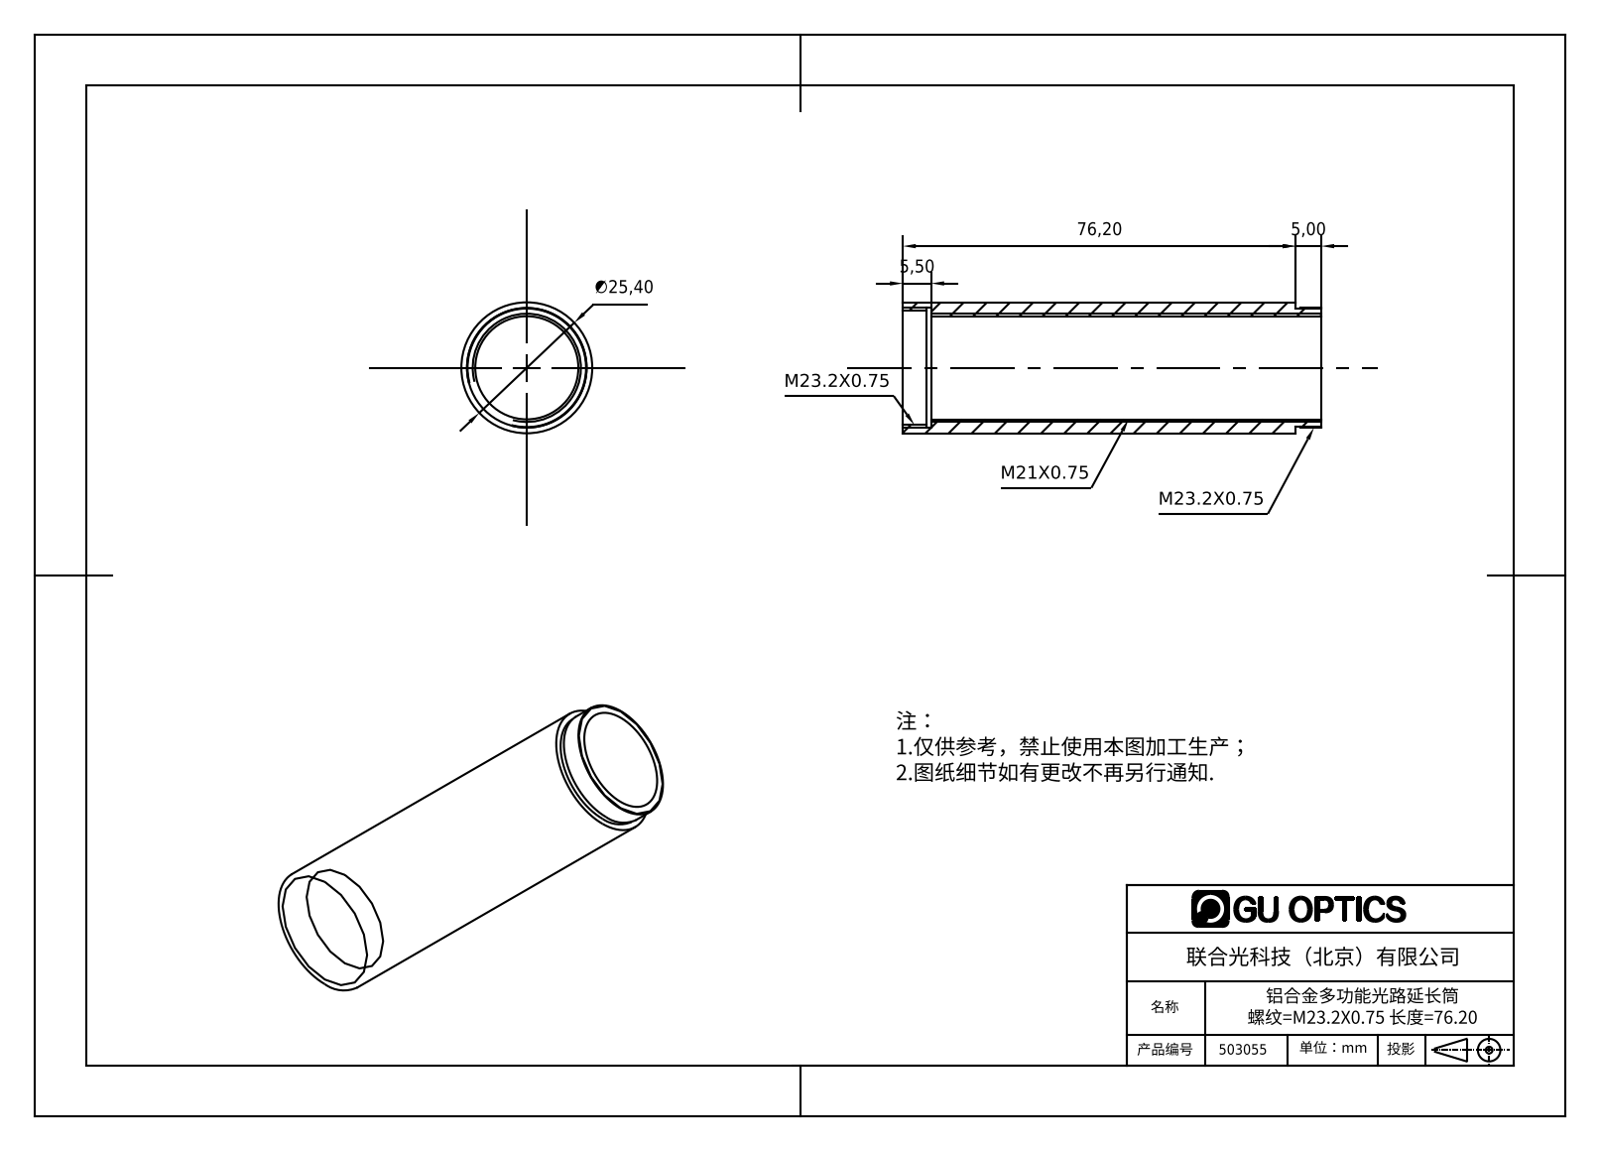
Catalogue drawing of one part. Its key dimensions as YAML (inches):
part_name: "503055"
step_written_by: "SolidWorks 2016 (AUTOMOTIVE_DESIGN)"
units: inches
bodies: {solids: 1, faces: 18, planar: 6, cylindrical: 12, other: 0}
overall_size: [3.197, 1, 1]
volume: 0.901
surface_area: 18.71
round_holes:
  - {diameter: 0.787, count: 1}
  - {diameter: 0.874, count: 1}
  - {diameter: 0.921, count: 1}
round_bosses_or_shafts:
  - {diameter: 1, count: 1}
  - {diameter: 0.913, count: 1}
  - {diameter: 0.906, count: 1}
face_to_face_distances: [0.217, 3.197, 2.98, 3, 2.783, 0.197, 0.039, 2.823, 0.177, 3.02]
